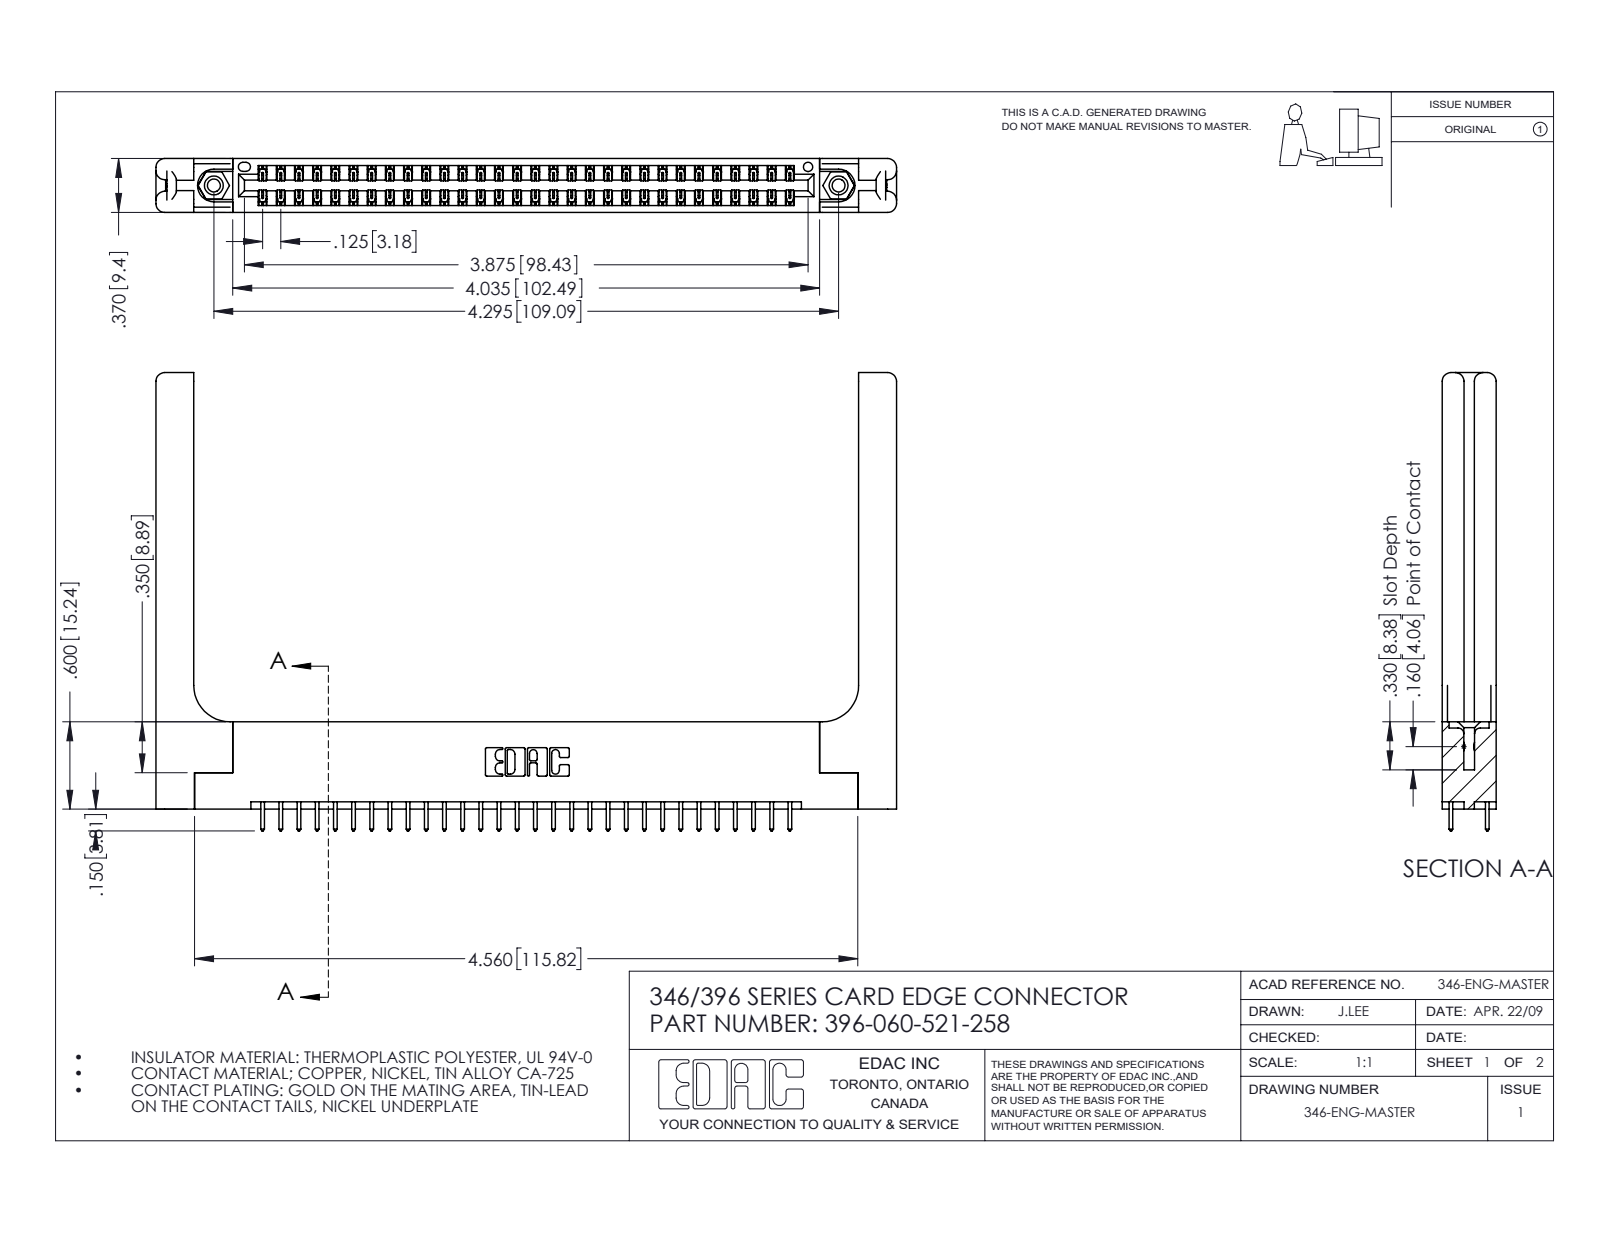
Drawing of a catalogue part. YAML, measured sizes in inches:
part_name: "396-060-521-258; 345-292-001_345-293-121; 346 Part_Flush Mounting Lugs - 0.156 Dia-TH; 346-220-058_345-220-058 (+1 more)"
step_written_by: "SolidWorks 2016 (CONFIG_CONTROL_DESIGN)"
units: inches
bodies: {solids: 65, faces: 3498, planar: 2324, cylindrical: 1114, other: 60}
overall_size: [5.091, 3.15, 0.37]
volume: 1.22
surface_area: 33.77
round_holes:
  - {diameter: 0.089, count: 2}
  - {diameter: 0.125, count: 2}
  - {diameter: 0.156, count: 2}
  - {diameter: 0.064, count: 1}
round_bosses_or_shafts:
  - {diameter: 0.155, count: 2}
partial_cylinders:
  - {radius: 0.006, count: 90}
  - {radius: 0.01, count: 60}
  - {radius: 0.01, count: 22}
  - {radius: 0.06, count: 16}
  - {radius: 0.007, count: 6}
  - {radius: 0.031, count: 6}
  - {radius: 0.026, count: 3}
  - {radius: 0.014, count: 2}
face_to_face_distances: [0.37, 0.048, 0.322, 0.072, 0.148, 0.15, 0.25, 0.025, 0.298, 0.275]
hole_center_spacings: [0.246, 4.087, 4.295]
